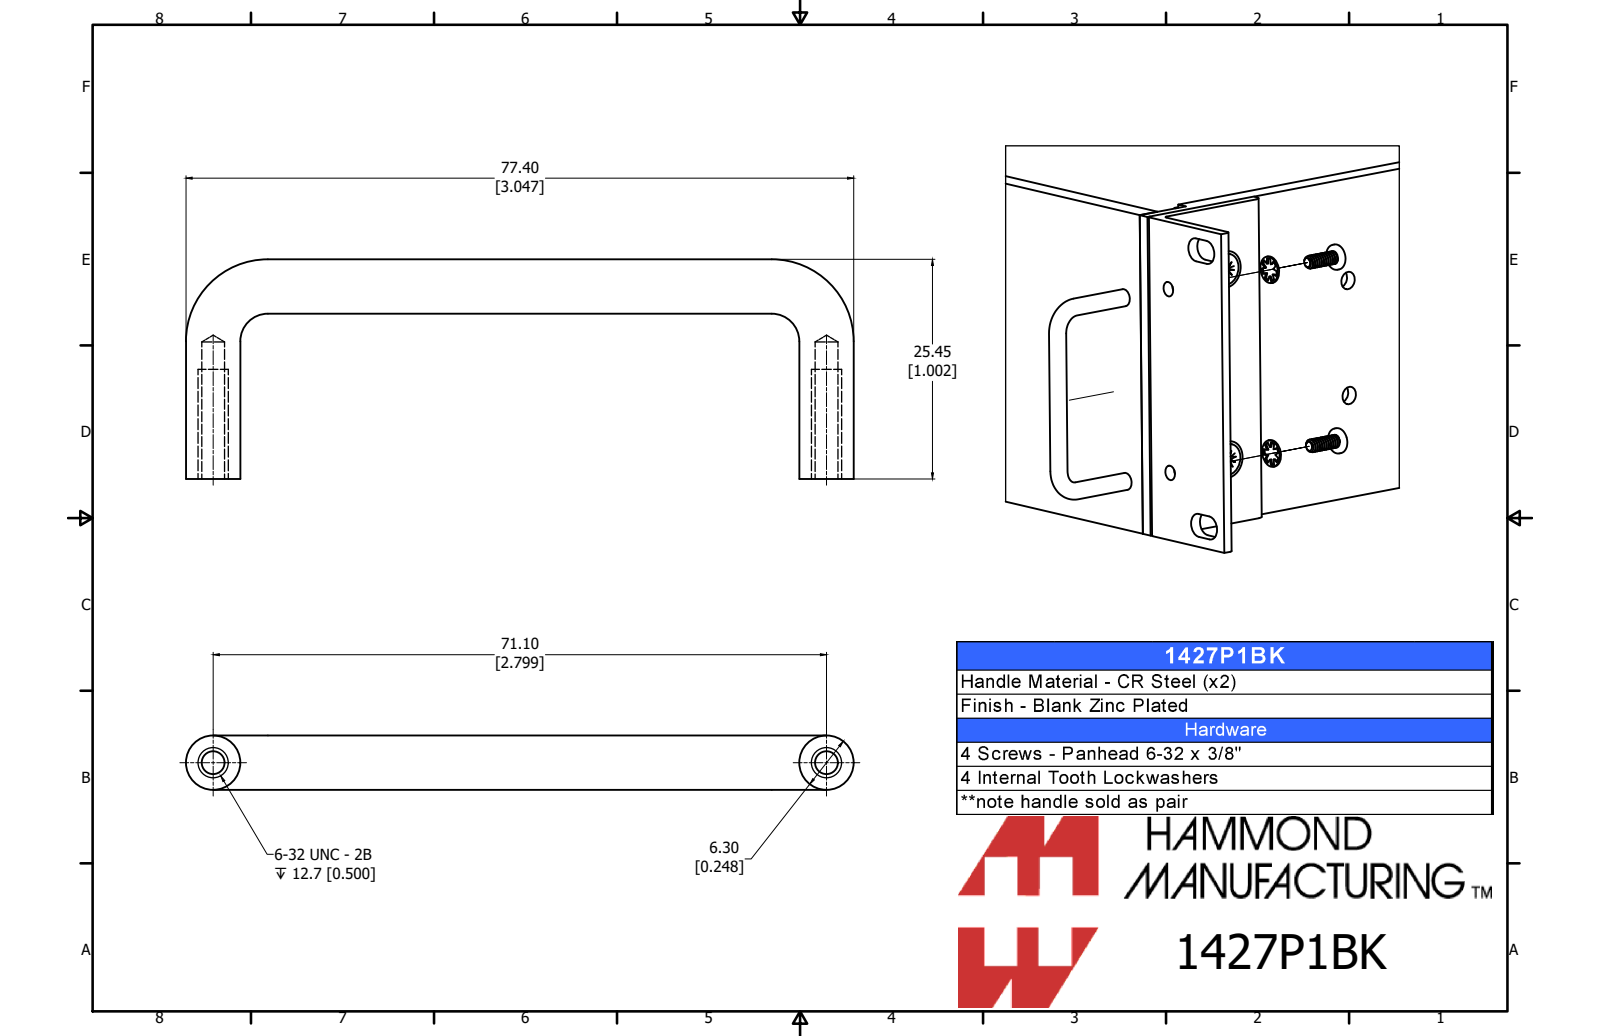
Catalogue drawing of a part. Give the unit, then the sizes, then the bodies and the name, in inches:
Units: inches
Overall size (bounding box): 3.047 × 1.002 × 0.248
Round holes (diameter × count): ⌀0.104 ×2
Round bosses / shafts (diameter × count): ⌀0.248 ×3
Hole centre spacings: 2.799
Volume: 0.199 in³ · Surface area: 3.891 in²
Bodies: 1 solid, 11 faces (2 planar, 5 cylindrical, 4 other)
Part name (STEP PRODUCT): 1427P1BK
STEP written by: SolidWorks 2021 (AUTOMOTIVE_DESIGN)
